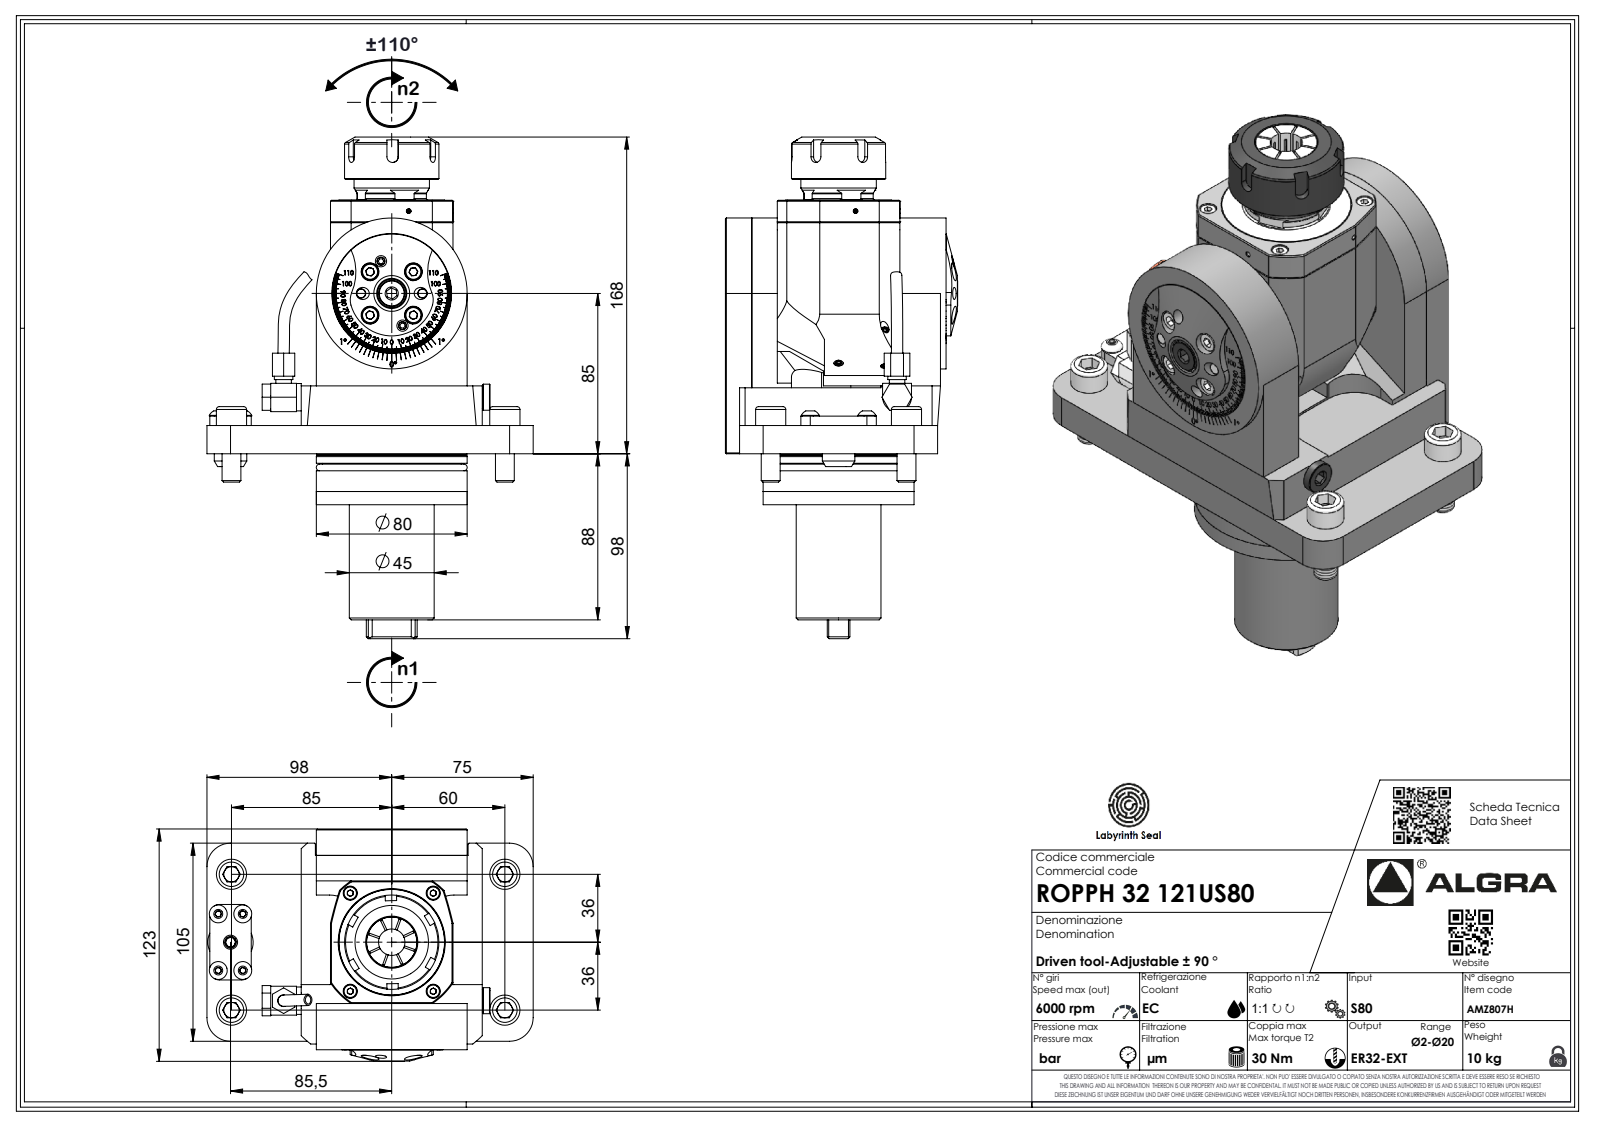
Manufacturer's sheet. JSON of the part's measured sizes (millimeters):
{"part_name": "ROPPH32121US80", "step_written_by": "SolidWorks 2023 (AUTOMOTIVE_DESIGN)", "units": "millimeters", "bodies": {"solids": 1, "faces": 571, "planar": 344, "cylindrical": 87, "other": 140}, "overall_size": [265.91, 173, 123], "volume_mm3": 1480000, "surface_area_mm2": 131533, "round_holes": [[2.1, 1]], "round_bosses_or_shafts": [[80, 2], [79.6, 1], [73.6, 1], [50, 1], [45, 1], [40, 1], [17.2, 1], [14.5, 1]], "partial_cylinders_radius": [[0.33, 7], [0.52, 7], [3.7, 7], [3, 5], [5, 4], [12.5, 4], [10, 2], [12, 2]], "face_to_face_distances": [15, 7.5, 65, 20, 27, 88, 42, 24.5, 72.5, 27.5]}
